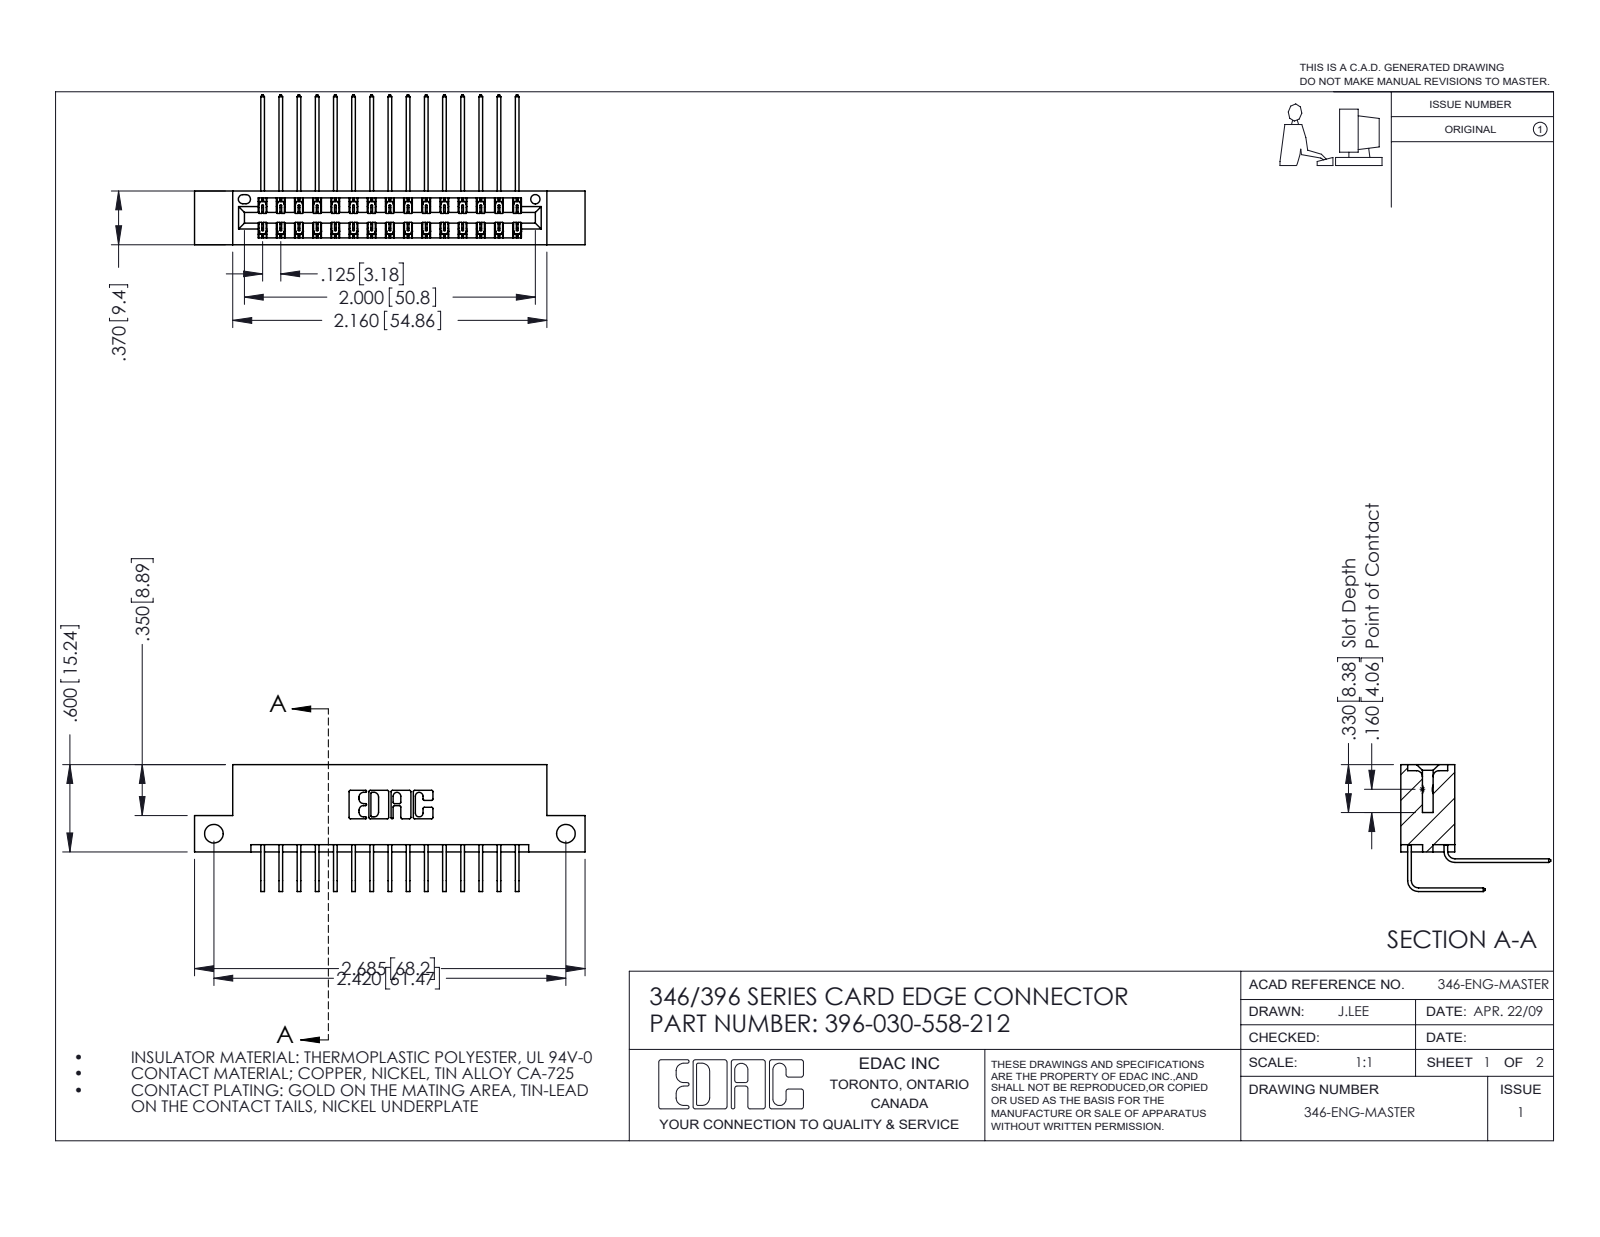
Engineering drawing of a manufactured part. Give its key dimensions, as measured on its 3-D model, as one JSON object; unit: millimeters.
{"part_name": "396-030-558-212; 345-292-001_558 Tail - 2; 345-292-001_558 559 Tail - 1; 346 Part_Flush Mounting Lugs - Side Mount", "step_written_by": "SolidWorks 2016 (CONFIG_CONTROL_DESIGN)", "units": "millimeters", "bodies": {"solids": 31, "faces": 1742, "planar": 1186, "cylindrical": 556, "other": 0}, "overall_size": [68.2, 26.2, 22.2], "volume_mm3": 6520, "surface_area_mm2": 9239, "round_holes": [[3.3, 2], [1.6, 1]], "partial_cylinders_radius": [[0.2, 45], [0.3, 22], [0.2, 6], [0.8, 6], [0.7, 3], [0.4, 2], [0.6, 2], [0.6, 2]], "face_to_face_distances": [8.2, 1.2, 6.4, 0.6, 9.4, 7.6, 1.8, 7, 3.8, 5.6], "hole_center_spacings": [61.5]}
